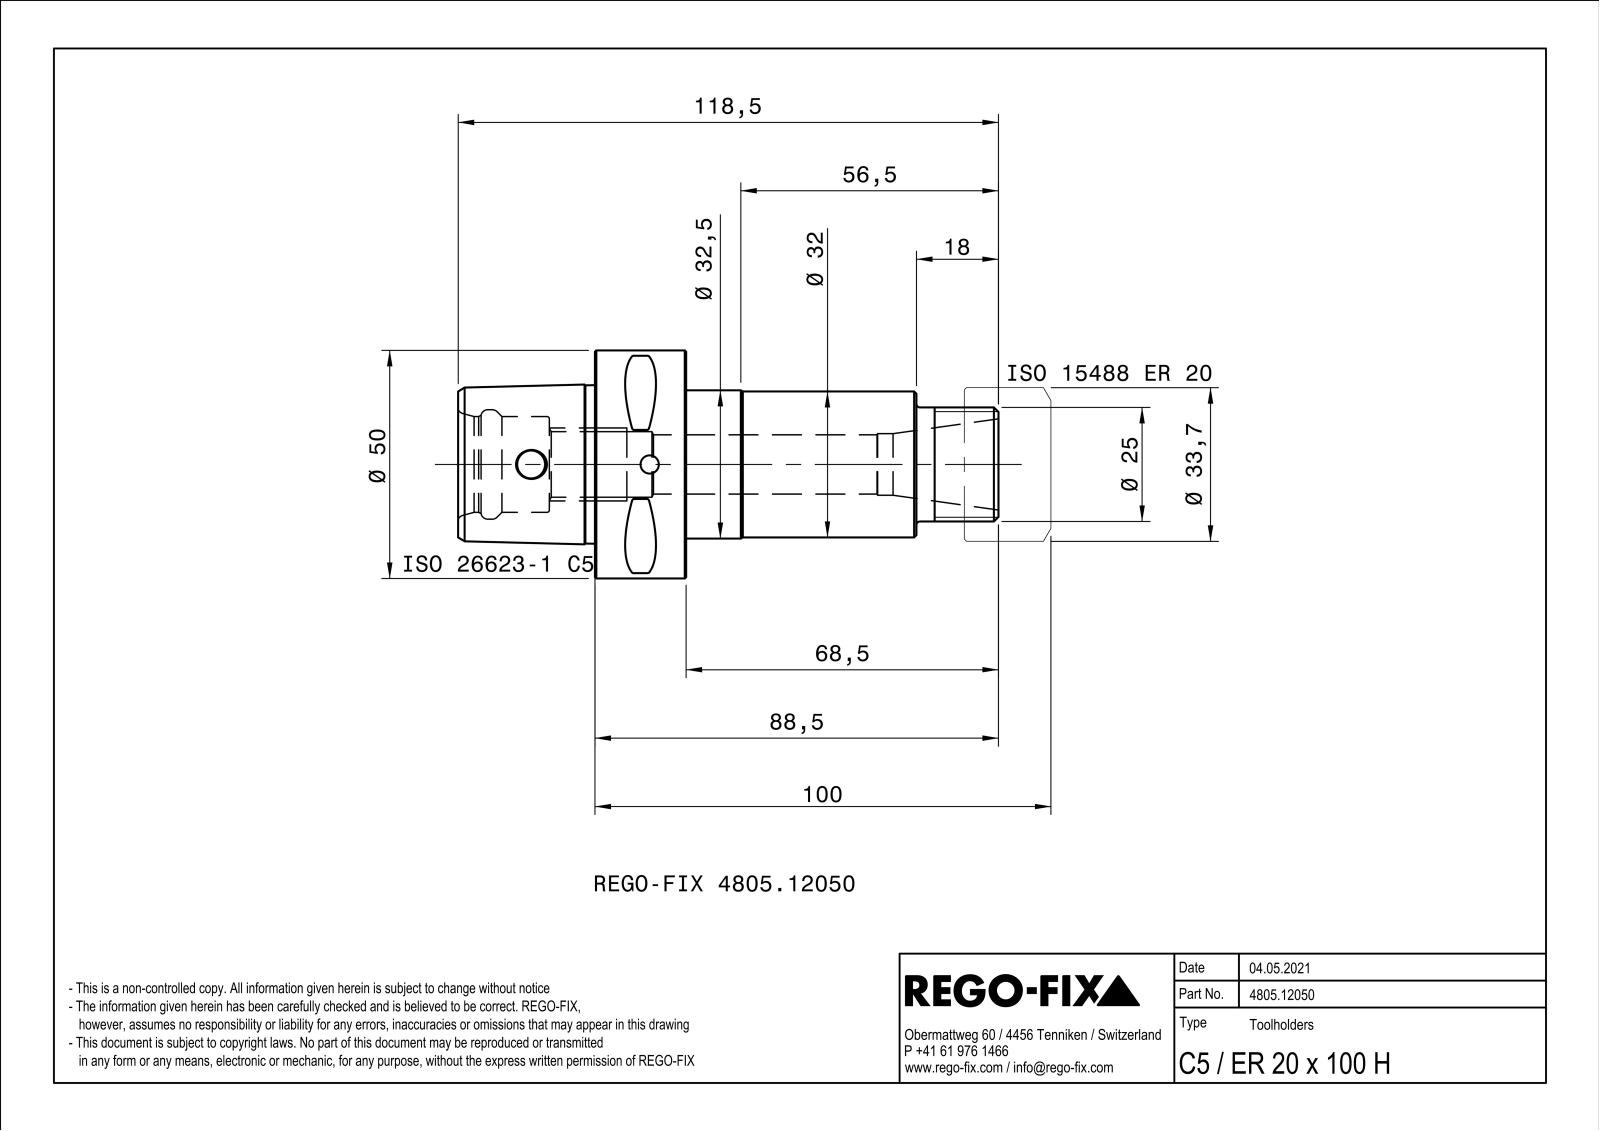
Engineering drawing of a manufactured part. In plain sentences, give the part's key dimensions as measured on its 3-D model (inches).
The part is named "NOCUT". Its 3-D file was written by "SIEMENS PLM Software Solid Edge ST10 (AUTOMOTIVE_DESIGN)". It is 1 solid with 112 faces: 21 planar, 26 cylindrical and 65 other. Overall it measures 4.665 by 1.969 by 1.969 inches. Its volume is 5.582 cubic inches and its surface area 34.49 square inches. Round holes: 1 of diameter 0.157, 1 of diameter 0.24, 1 of diameter 0.512, 1 of diameter 0.531, 1 of diameter 0.566, 1 of diameter 0.827, 1 of diameter 0.945. Round bosses or shafts: 1 of diameter 1.969, 1 of diameter 1.28, 1 of diameter 1.26, 1 of diameter 0.984. Partial cylindrical surfaces (rounded edges, fillets, slot ends): 8 of radius 0.02, 1 of radius 0.157. The main face-to-face distances are 0.787, 1.181, 1.969, 1.988, 2.776, 3.957, 0.755, 1.748, 3.169, 0.394. The hole center spacings are 1.024.
